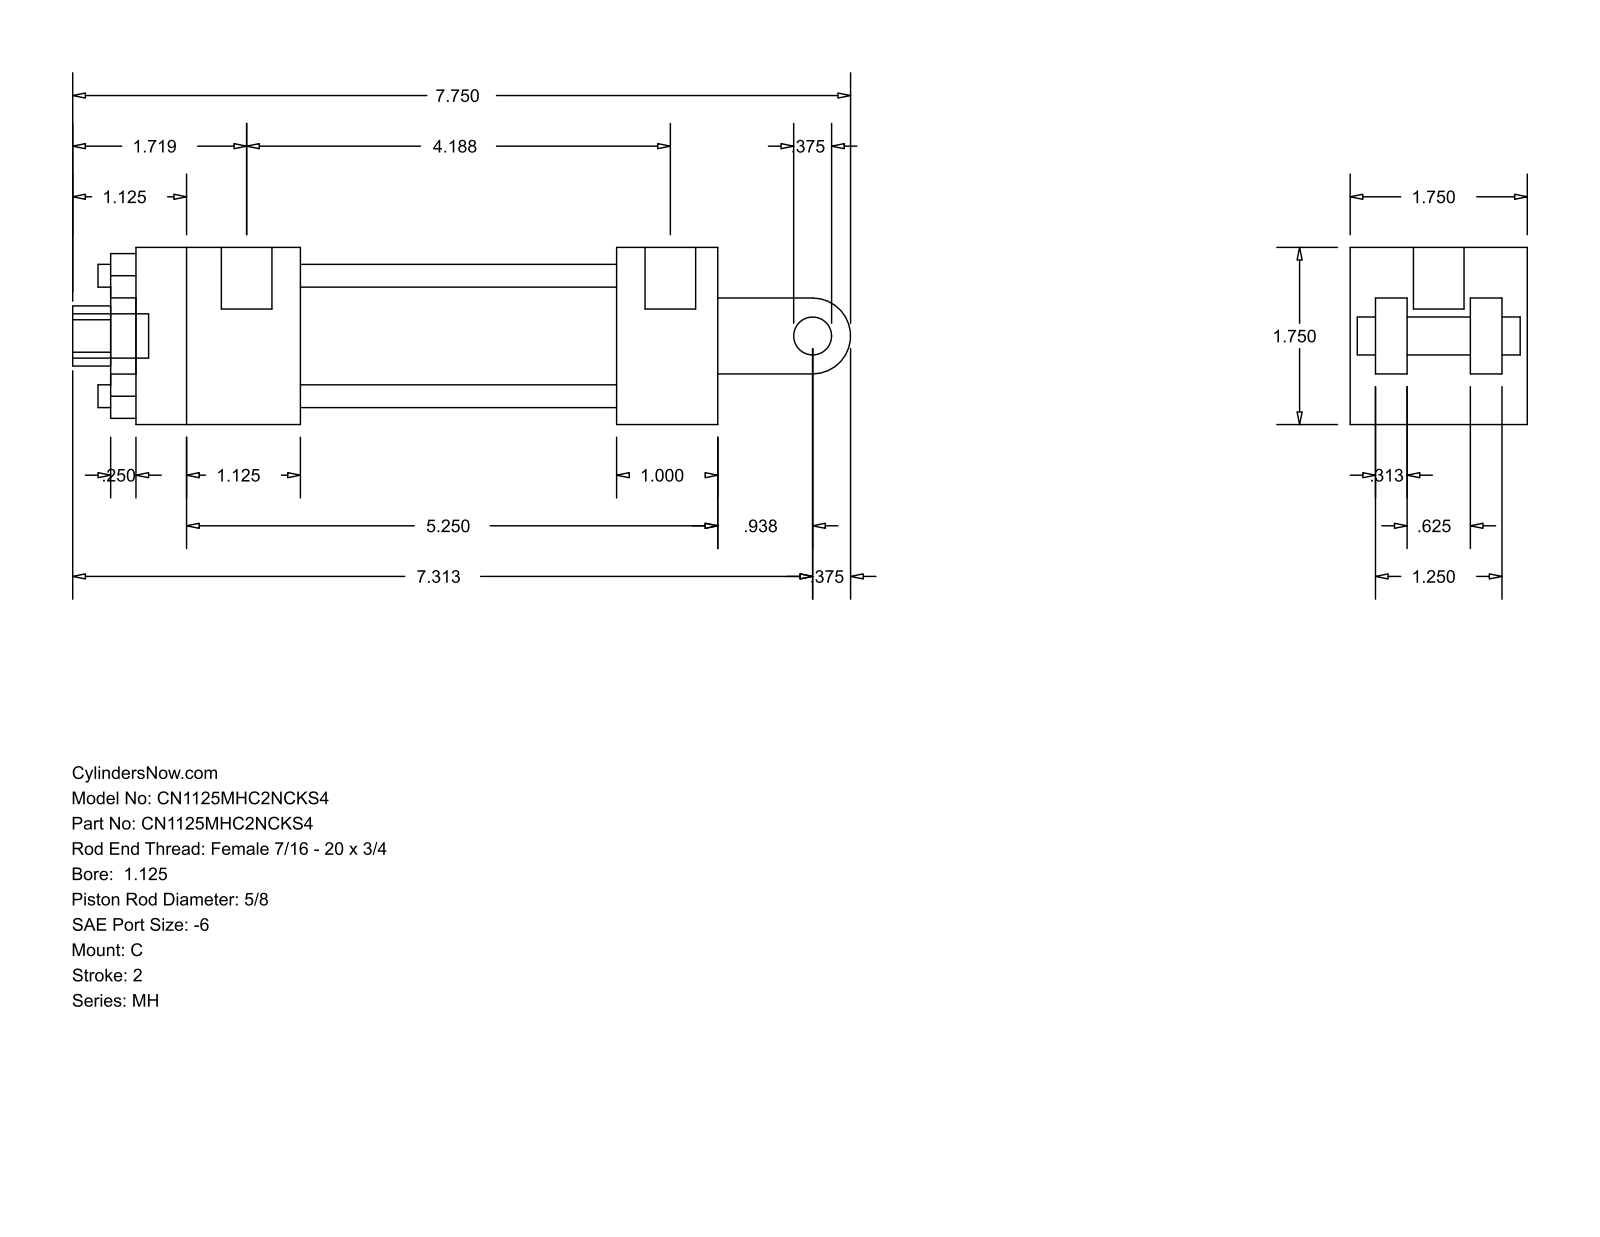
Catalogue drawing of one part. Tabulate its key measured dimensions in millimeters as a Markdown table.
| quantity | value |
| --- | --- |
| part name | MH_C__0112_0.625 |
| STEP written by | GSSL Pune (CONFIG_CONTROL_DESIGN) |
| units | millimeters |
| bodies | 0 solids, 99 faces (70 planar, 29 cylindrical, 0 other) |
| overall size | 195.26 × 44.45 × 44.45 |
| round holes (diameter × count) | 5.71 × 4, 5.56 × 2, 12.7 × 1, 15.88 × 1, 28.57 × 1, 34.92 × 1 |
| round bosses / shafts (diameter × count) | 5.56 × 2, 12.7 × 1, 11.11 × 1, 9.53 × 1 |
| partial cylindrical surfaces (radius × count) | 7.54 × 1, 9.53 × 1 |
| main face-to-face distances | 44.46, 6.35, 31.76, 14.29, 12.7, 30.17, 38.11, 7.94, 23.82, 25.4 |
| hole center spacings | 21.37, 30.22, 42.74 |
